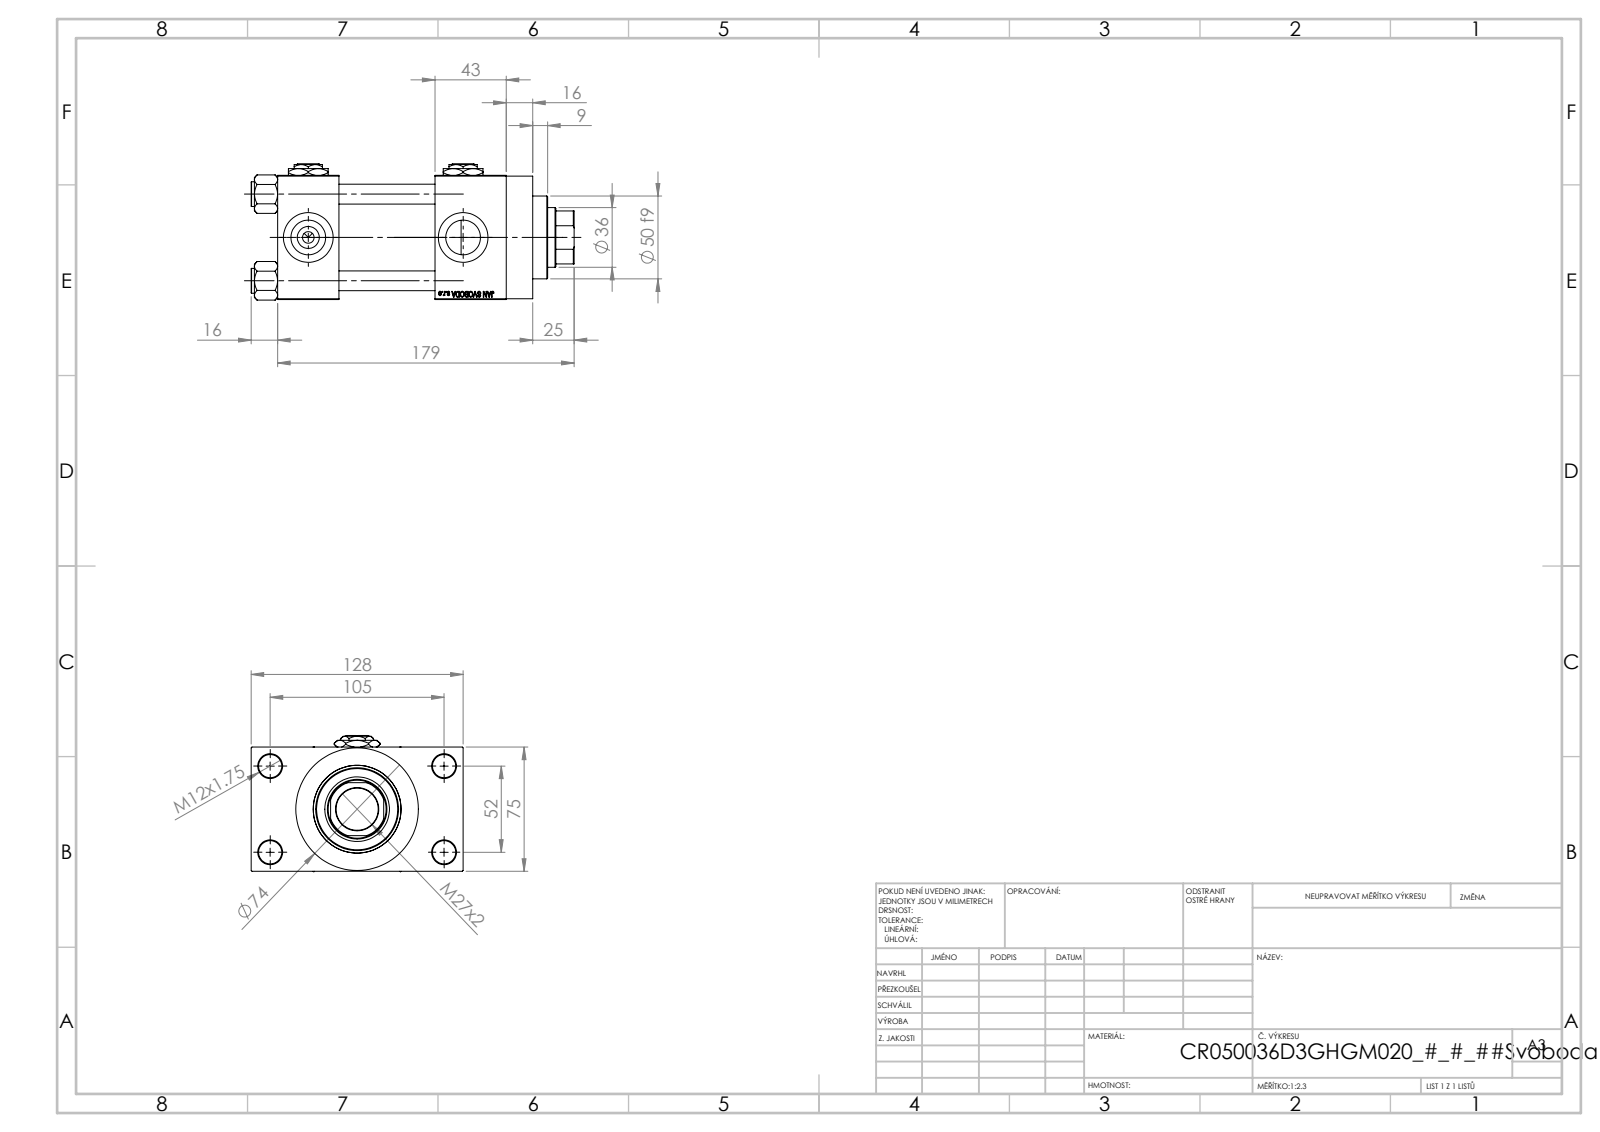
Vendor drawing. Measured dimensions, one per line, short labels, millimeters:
name: V215CR_D_Body; NUT_M5_D; V215_VC_A; Zatka_pro_OIL_PORT (+2 more)
written by: SolidWorks 2019 (CONFIG_CONTROL_DESIGN)
unit: mm
bodies: 12 solids, 1202 faces (544 planar, 99 cylindrical, 559 other)
size: 195 × 128 × 82.27
volume: 289 913 mm³; area: 179 757 mm²
holes: 4× ⌀12, 4× ⌀14, 4× ⌀20.96, 4× ⌀30, 3× ⌀7, 1× ⌀25.5, 1× ⌀36, 1× ⌀39, 1× ⌀41, 1× ⌀53
bosses: 4× ⌀15, 1× ⌀74, 1× ⌀56, 1× ⌀50
rounds: 1× R17.5
face distances: 75, 58, 37, 95, 26.5, 138, 43, 101, 101.5, 16
hole spacings: 26.35, 36.98, 52.3, 58.43, 58.59, 78.65, 94.37, 52
